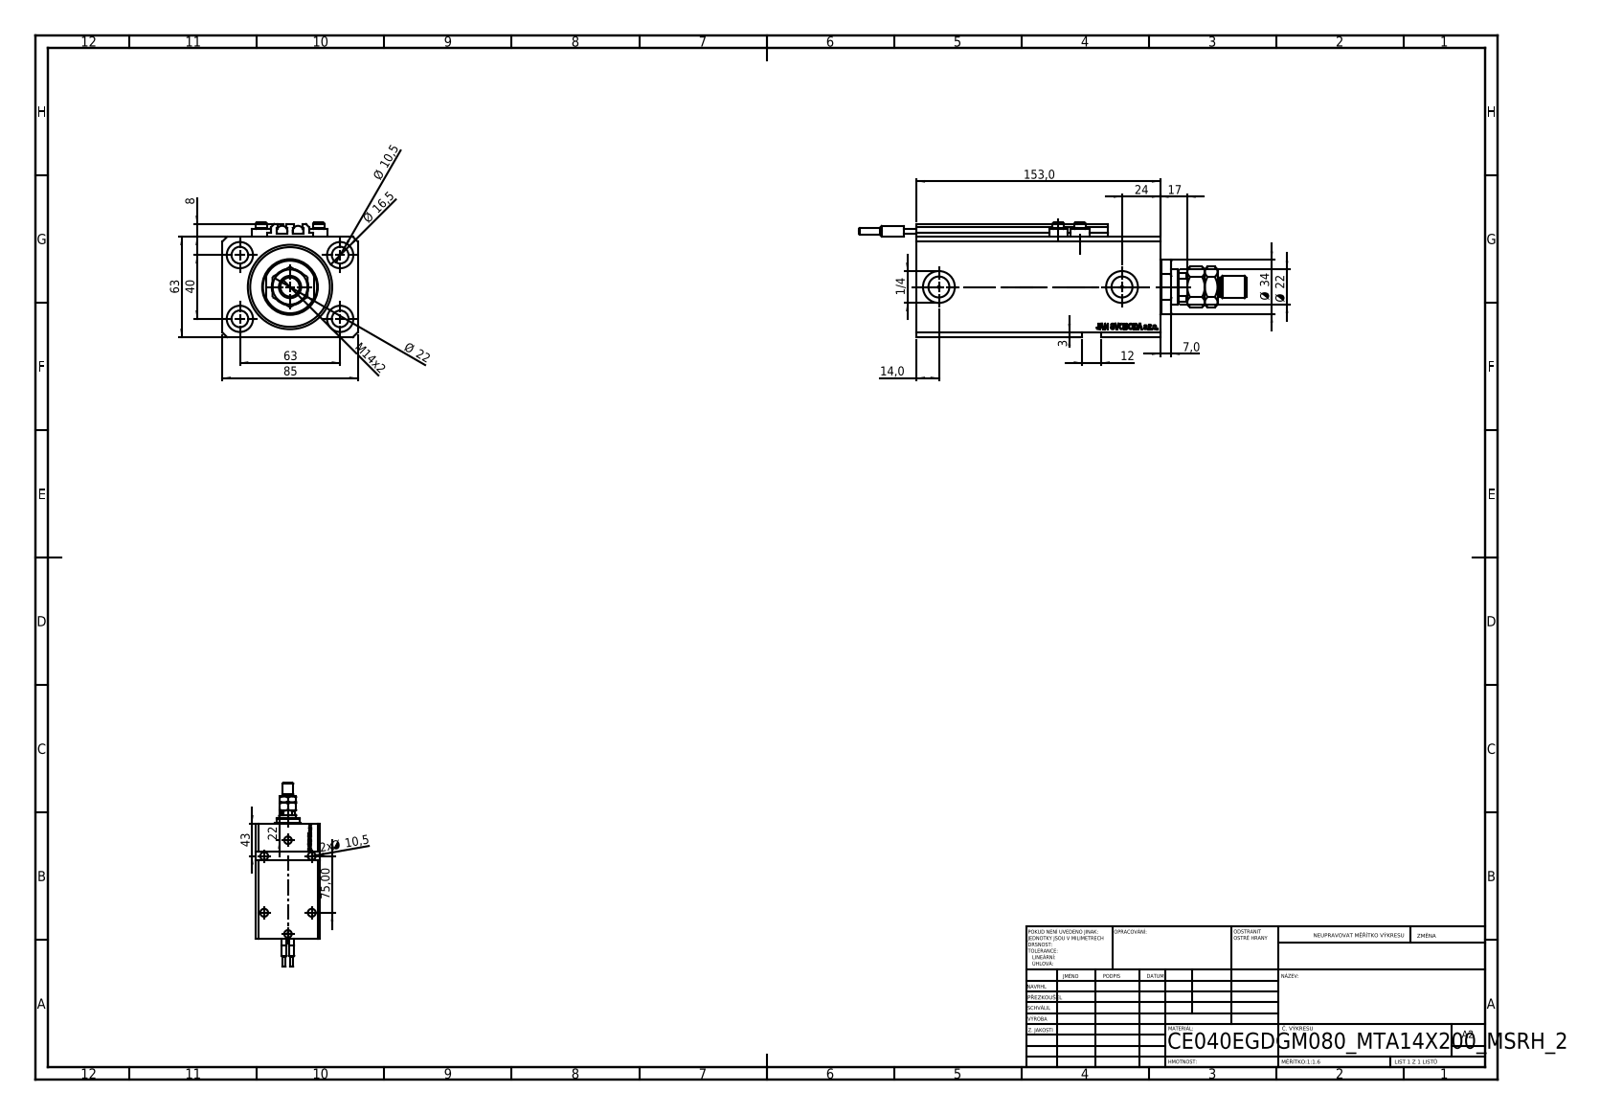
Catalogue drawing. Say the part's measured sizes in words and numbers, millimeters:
The part is named "MTA; V250CE_C_VCP; V250CE_E_Body; V250CE_VC_E (+2 more)". Its 3-D file was written by "SolidWorks 2019 (CONFIG_CONTROL_DESIGN)". It is 11 solids with 1224 faces: 586 planar, 174 cylindrical and 464 other. Overall it measures 243 by 85 by 72 millimeters. Its volume is 694 339 cubic millimeters and its surface area 147 771 square millimeters. Round holes: 8 of diameter 10.5, 4 of diameter 1.25, 4 of diameter 4, 4 of diameter 16.5, 2 of diameter 10, 2 of diameter 13.16, 2 of diameter 20, 1 of diameter 12.5, 1 of diameter 22, 1 of diameter 40, 1 of diameter 53. Round bosses or shafts: 4 of diameter 11.6, 4 of diameter 7, 2 of diameter 6.8, 2 of diameter 6.5, 2 of diameter 4, 1 of diameter 34, 1 of diameter 14, 1 of diameter 12. Partial cylindrical surfaces (rounded edges, fillets, slot ends): 10 of radius 0.2, 1 of radius 10.5. The main face-to-face distances are 63, 85, 17, 153, 136, 65, 11.4, 124.6, 141.6, 3. The hole center spacings are 37.31, 63, 13.6, 15.4, 24.96, 33.62, 36, 37.86.
